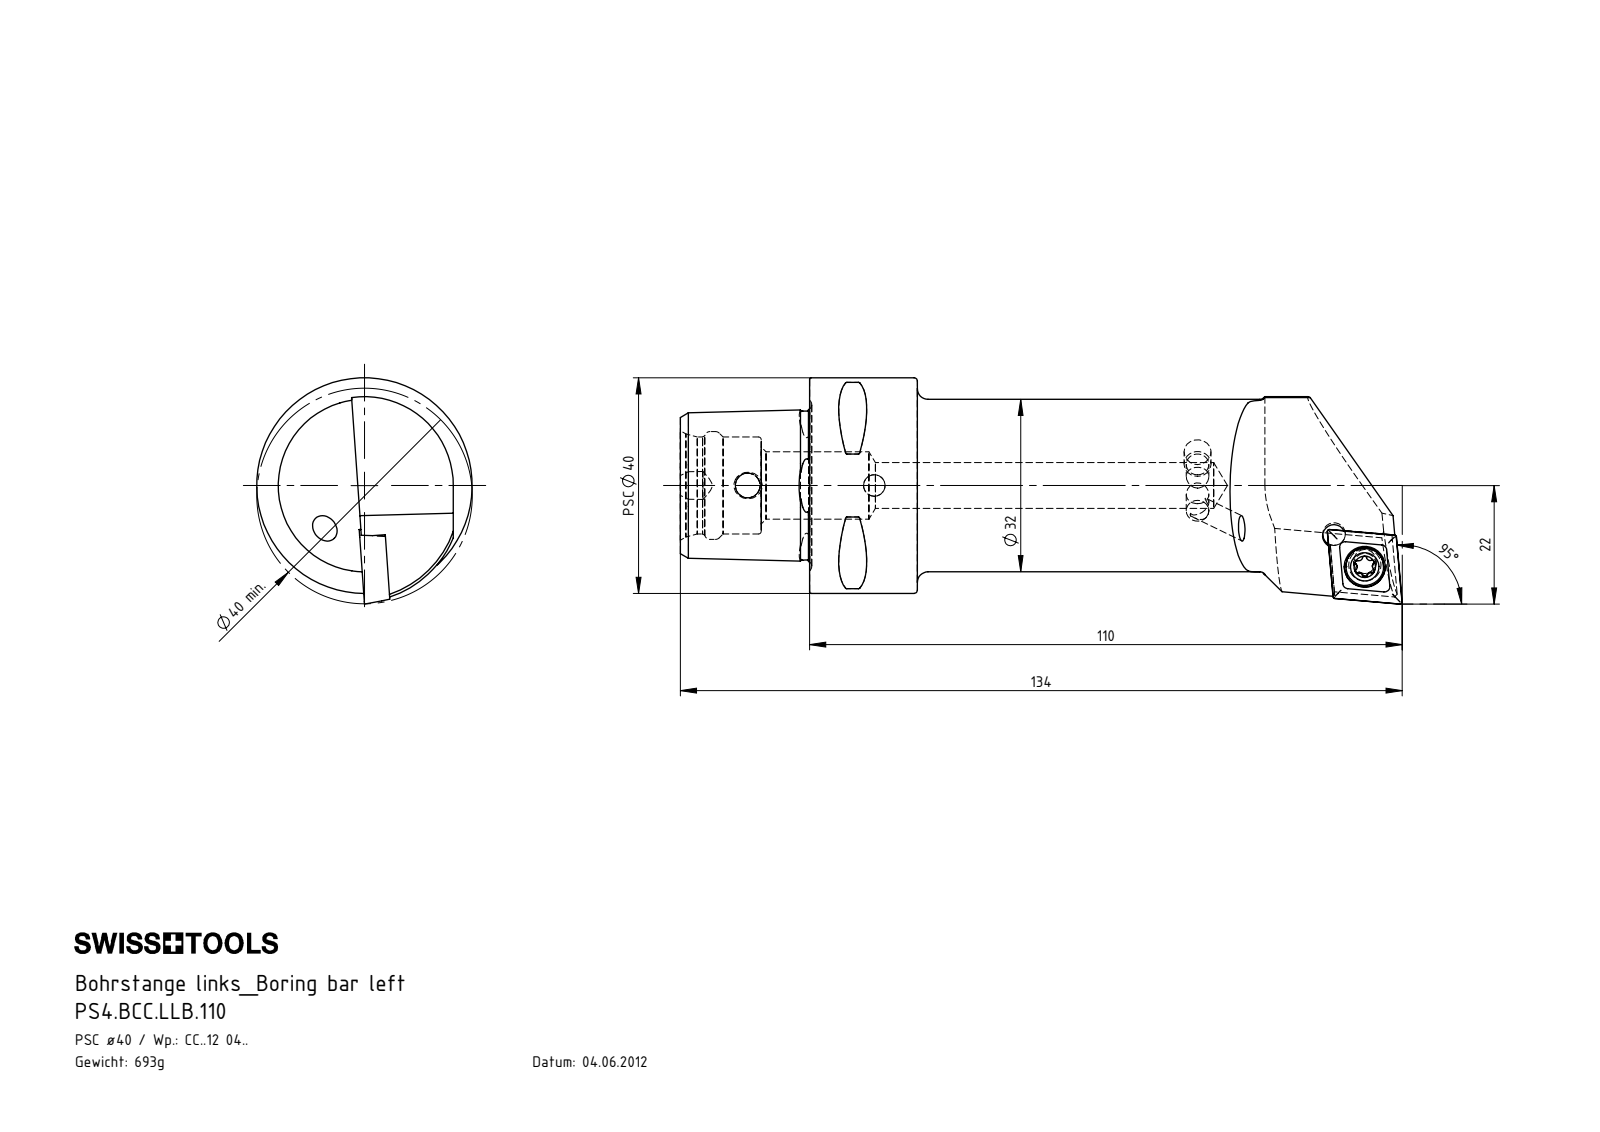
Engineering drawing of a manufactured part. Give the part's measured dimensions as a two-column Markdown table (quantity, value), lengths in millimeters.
| quantity | value |
| --- | --- |
| part name | CCMT120404; KVT_MB_600_050; PS4-BCC.LLB.110_A; WCC-ER2.001.010_A (+1 more) |
| STEP written by | SolidWorks 2012 (CONFIG_CONTROL_DESIGN) |
| units | millimeters |
| bodies | 5 solids, 291 faces (50 planar, 75 cylindrical, 166 other) |
| overall size | 134 × 42 × 40 |
| volume | 88 616 mm³ |
| surface area | 20 026 mm² |
| round holes (diameter × count) | 4.2 × 4, 4 × 2, 4.6 × 1, 5 × 1, 5.5 × 1, 7.6 × 1, 8.5 × 1, 12.5 × 1, 18 × 1, 20 × 1 |
| round bosses / shafts (diameter × count) | 5 × 2, 40 × 1, 32 × 1, 7 × 1 |
| partial cylindrical surfaces (radius × count) | 0.3 × 8, 0.39 × 6, 0.69 × 6, 3 × 2, 16.5 × 1, 19 × 1 |
| main face-to-face distances | 20, 4.46, 24, 44, 15.52, 35.3, 15, 9, 29, 4.76 |
| hole center spacings | 8.09, 23.5 |
